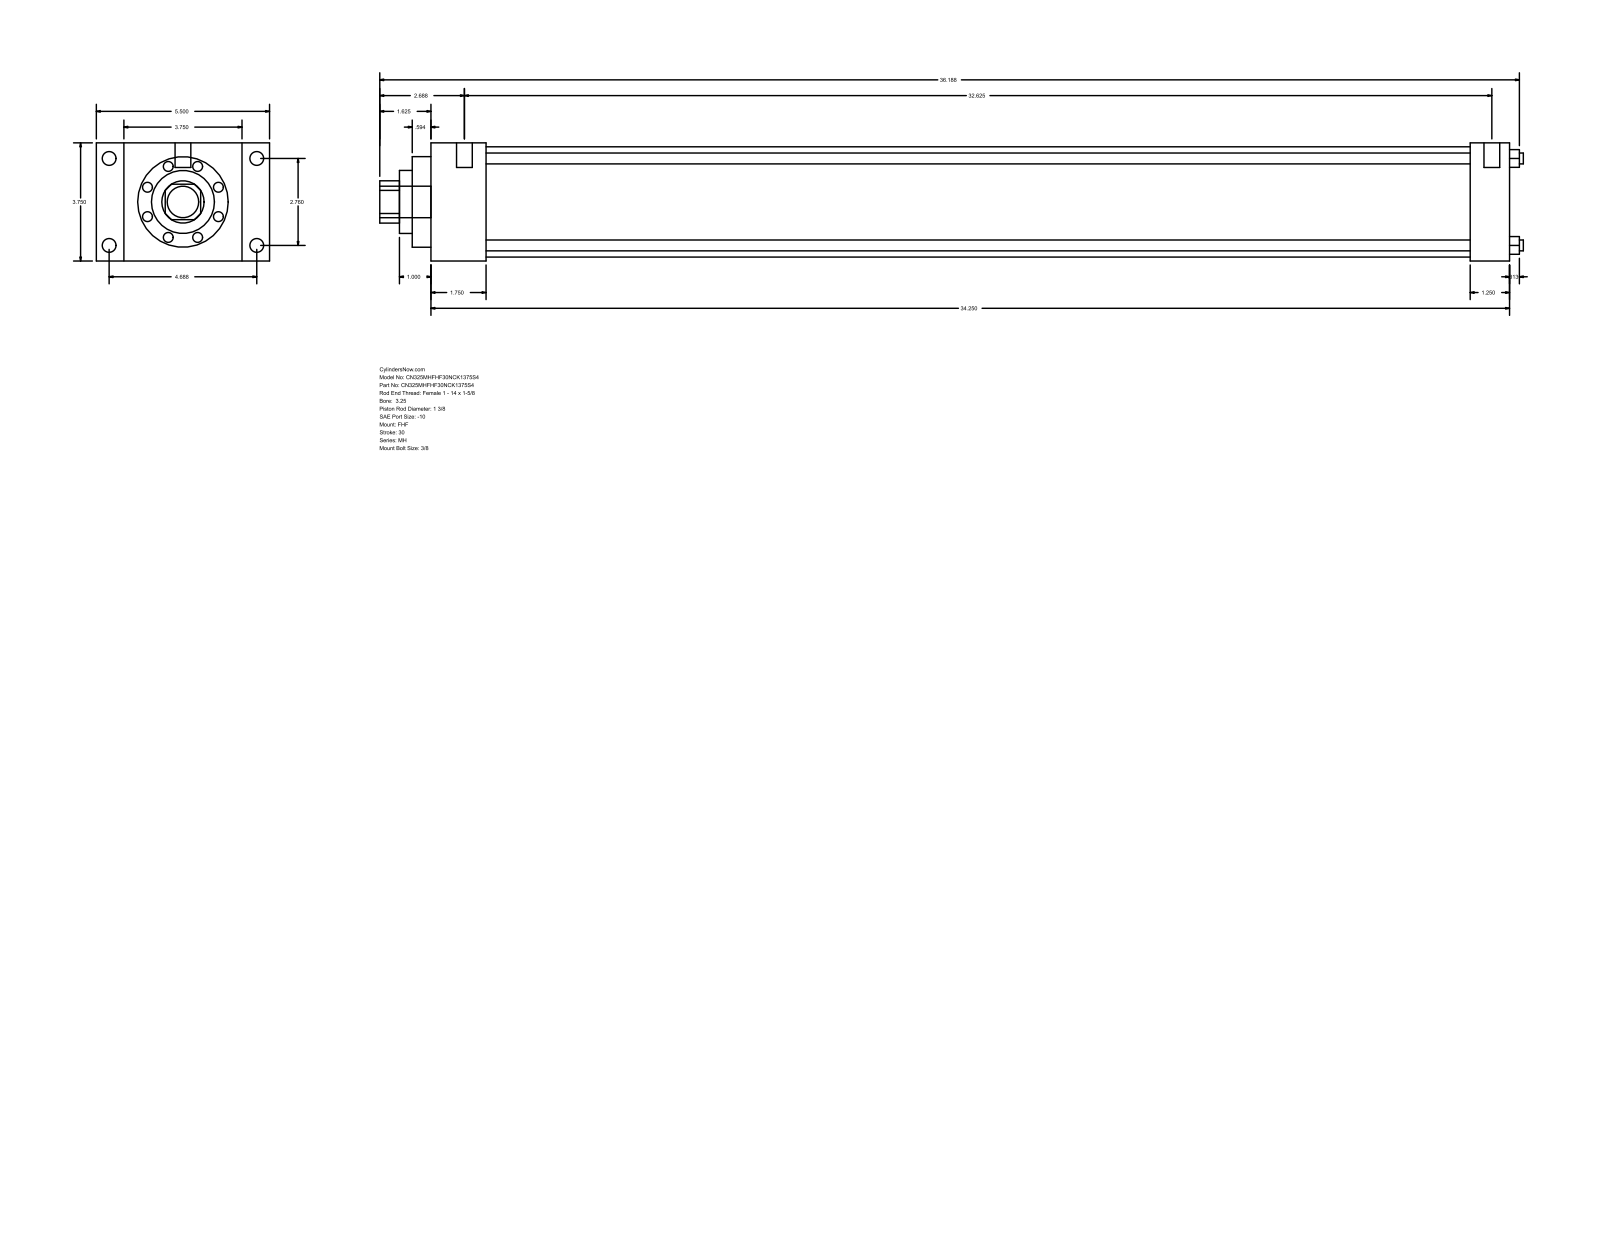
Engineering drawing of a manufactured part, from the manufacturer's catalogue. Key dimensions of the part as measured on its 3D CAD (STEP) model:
Part name (STEP PRODUCT): MH_FHF__0325_1.375
STEP written by: GSSL Pune (CONFIG_CONTROL_DESIGN)
Units: millimetres
Bodies: 0 solids, 90 faces (61 planar, 29 cylindrical, 0 other)
Overall size (bounding box): 922.34 × 139.7 × 95.25
Round holes (diameter × count): ⌀8.76 ×4, ⌀34.92 ×1, ⌀50.8 ×1, ⌀73.03 ×1, ⌀88.9 ×1
Round bosses / shafts (diameter × count): ⌀11.13 ×4, ⌀5.56 ×4, ⌀12.7 ×2, ⌀25.4 ×1
Partial cylindrical surfaces — rounded edges, fillets, slot ends (radius × count): R17.06 ×1
Main face-to-face distances: 95.24, 869.96, 44.45, 825.51, 22.23, 117.47, 139.7, 838.21, 793.76, 31.75
Hole centre spacings: 49.57, 70.1, 99.14
